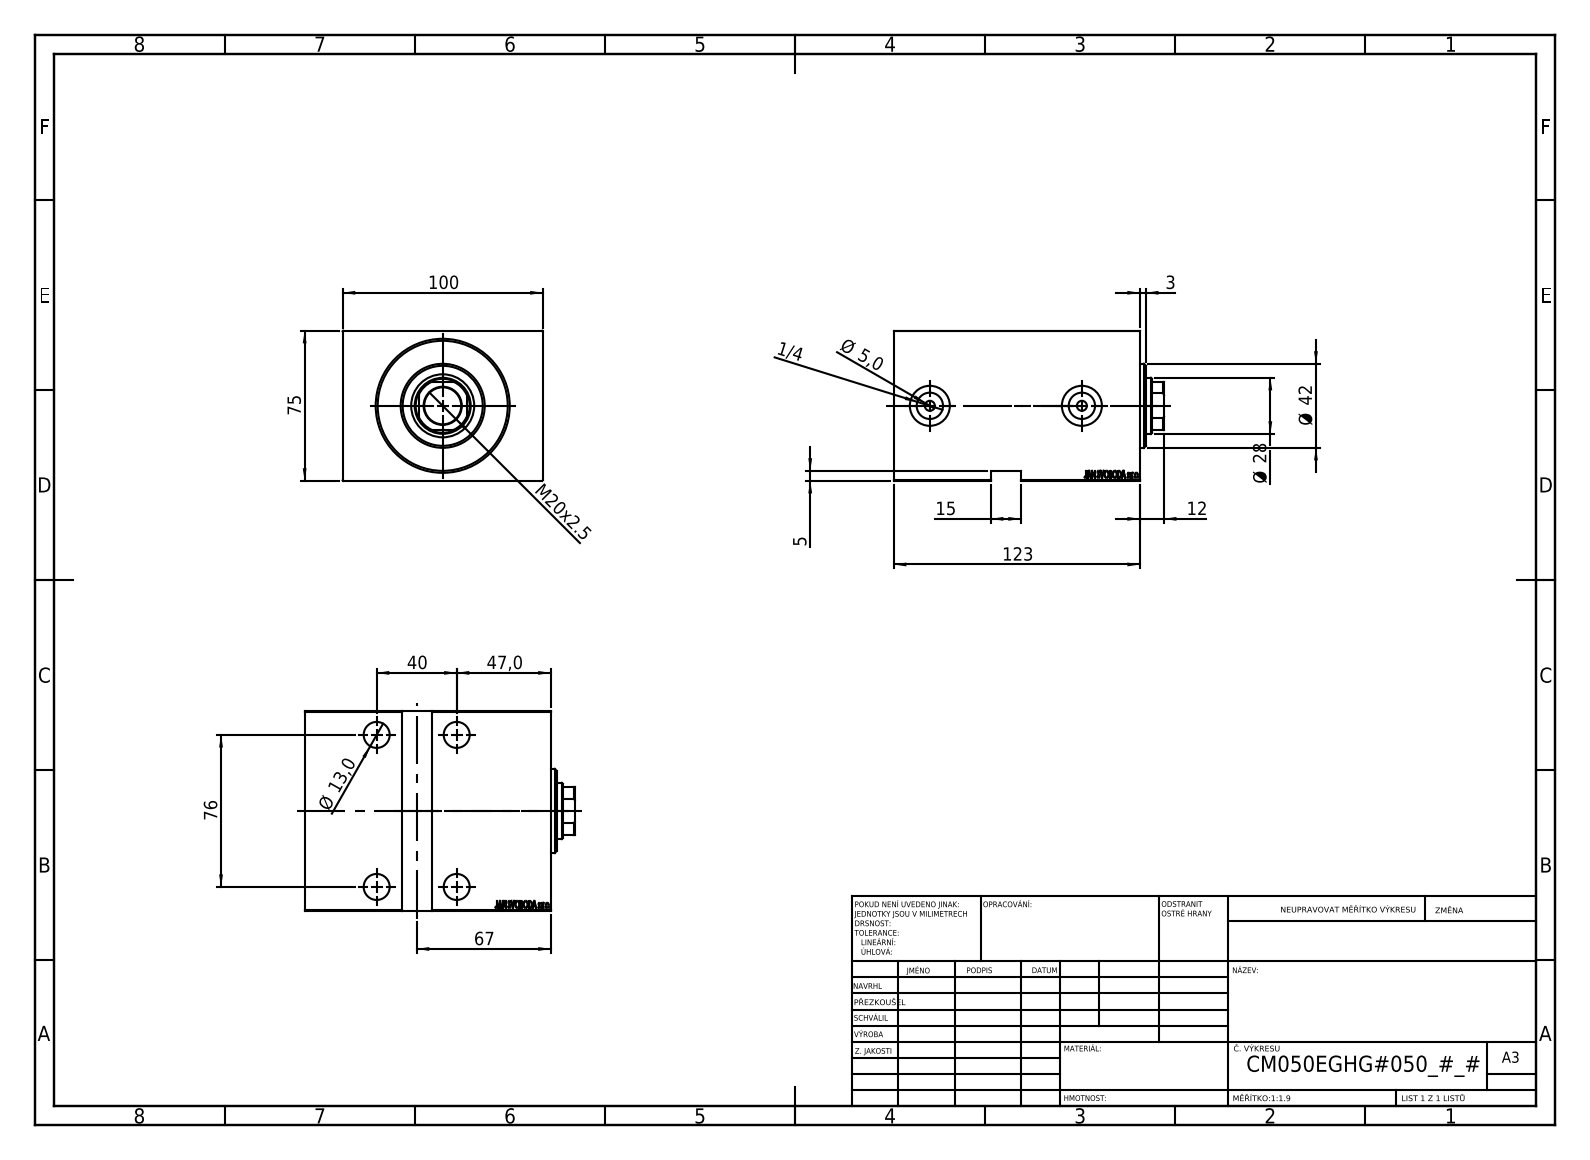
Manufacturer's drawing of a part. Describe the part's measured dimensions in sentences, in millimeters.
The part is named "V450CM_VC_B; V450CM_E_Body; V450CM_E_VCP". Its 3-D file was written by "SolidWorks 2019 (CONFIG_CONTROL_DESIGN)". It is 3 solids with 856 faces: 410 planar, 52 cylindrical and 394 other. Overall it measures 135 by 100 by 75 millimeters. Its volume is 799 931 cubic millimeters and its surface area 120 066 square millimeters. Round holes: 4 of diameter 13, 4 of diameter 19, 2 of diameter 5, 2 of diameter 13.16, 2 of diameter 20, 1 of diameter 18.5, 1 of diameter 28, 1 of diameter 31.5, 1 of diameter 50, 1 of diameter 65. Round bosses or shafts: 1 of diameter 52, 1 of diameter 42. Partial cylindrical surfaces (rounded edges, fillets, slot ends): 1 of radius 13.5. The main face-to-face distances are 75, 100, 123, 5, 14, 109, 118, 104, 61, 106.4. The hole center spacings are 76, 40, 85.88.
